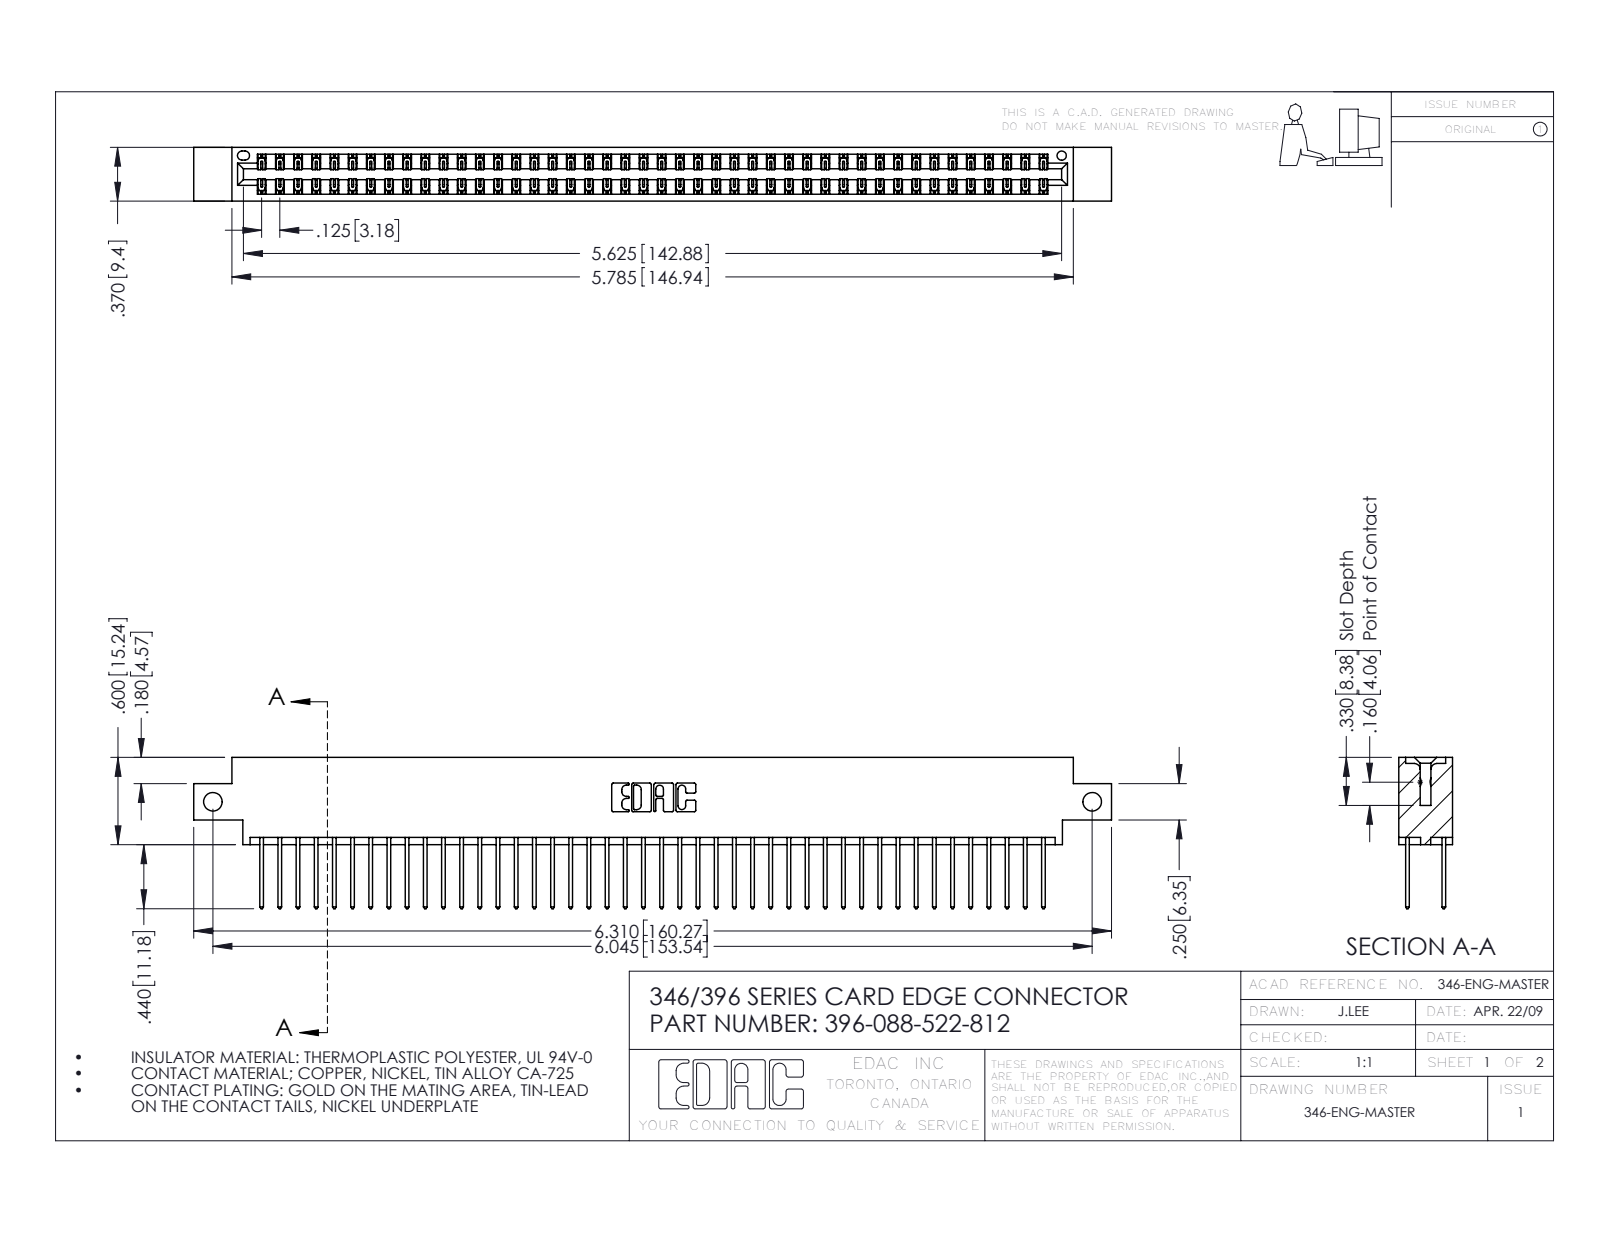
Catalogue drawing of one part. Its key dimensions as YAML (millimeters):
part_name: "346 Part_0.170 Offset - Side Mount; 396-088-522-812; 345-292-001_345-293-122"
step_written_by: "SolidWorks 2016 (CONFIG_CONTROL_DESIGN)"
units: millimeters
bodies: {solids: 89, faces: 4702, planar: 3160, cylindrical: 1542, other: 0}
overall_size: [160.3, 26.4, 9.4]
volume: 15600
surface_area: 22600
round_holes:
  - {diameter: 3.3, count: 2}
  - {diameter: 1.6, count: 1}
partial_cylinders:
  - {radius: 0.2, count: 132}
  - {radius: 0.3, count: 88}
  - {radius: 0.3, count: 22}
  - {radius: 0.2, count: 6}
  - {radius: 0.8, count: 6}
  - {radius: 0.7, count: 3}
  - {radius: 0.4, count: 2}
  - {radius: 0.6, count: 2}
face_to_face_distances: [1.2, 8.2, 6.4, 9.4, 1.8, 7.6, 0.6, 7, 3.8, 5.6]
hole_center_spacings: [153.5]
